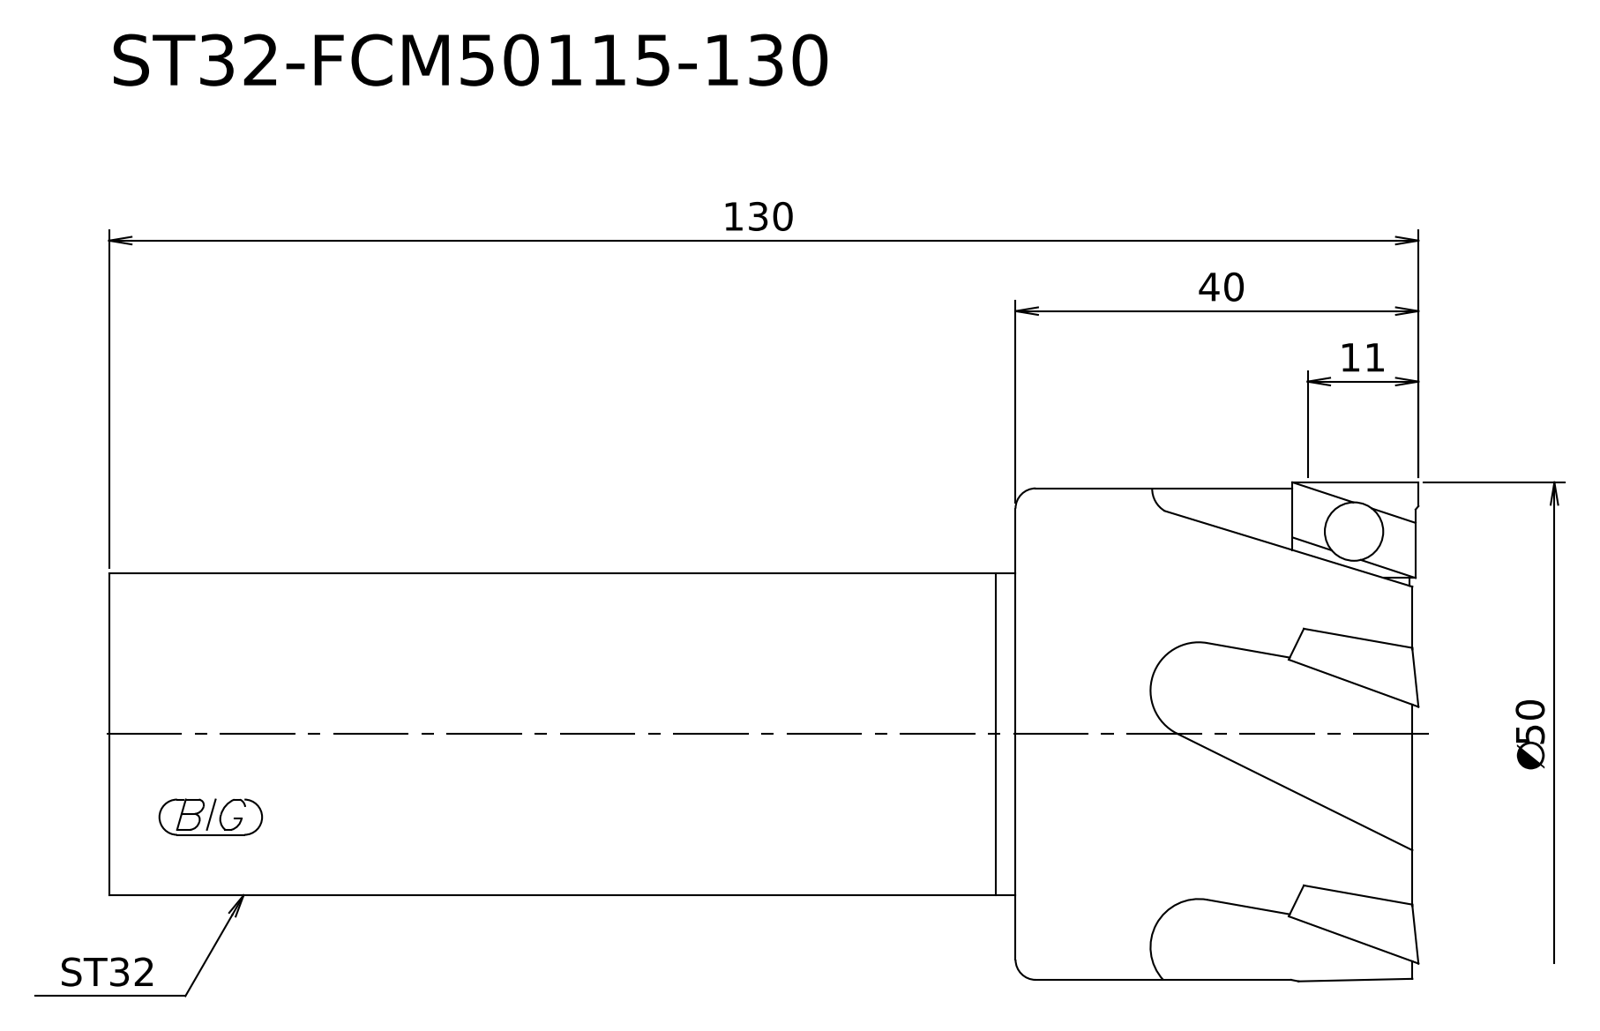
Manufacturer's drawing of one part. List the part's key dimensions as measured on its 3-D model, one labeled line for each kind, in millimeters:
STEP written by: Kubotek KeyCreator V8.5.1 (14335) (CONFIG_CONTROL_DESIGN)
Units: millimetres
Bodies: 1 solid, 7 faces (4 planar, 3 cylindrical, 0 other)
Overall size (bounding box): 130 × 50 × 50
Volume: 148 362 mm³ · Surface area: 19 154 mm²
Round bosses / shafts (diameter × count): ⌀50 ×1, ⌀48.8 ×1, ⌀32 ×1
Main face-to-face distances: 40, 130, 90, 12.51, 27.49, 117.49
